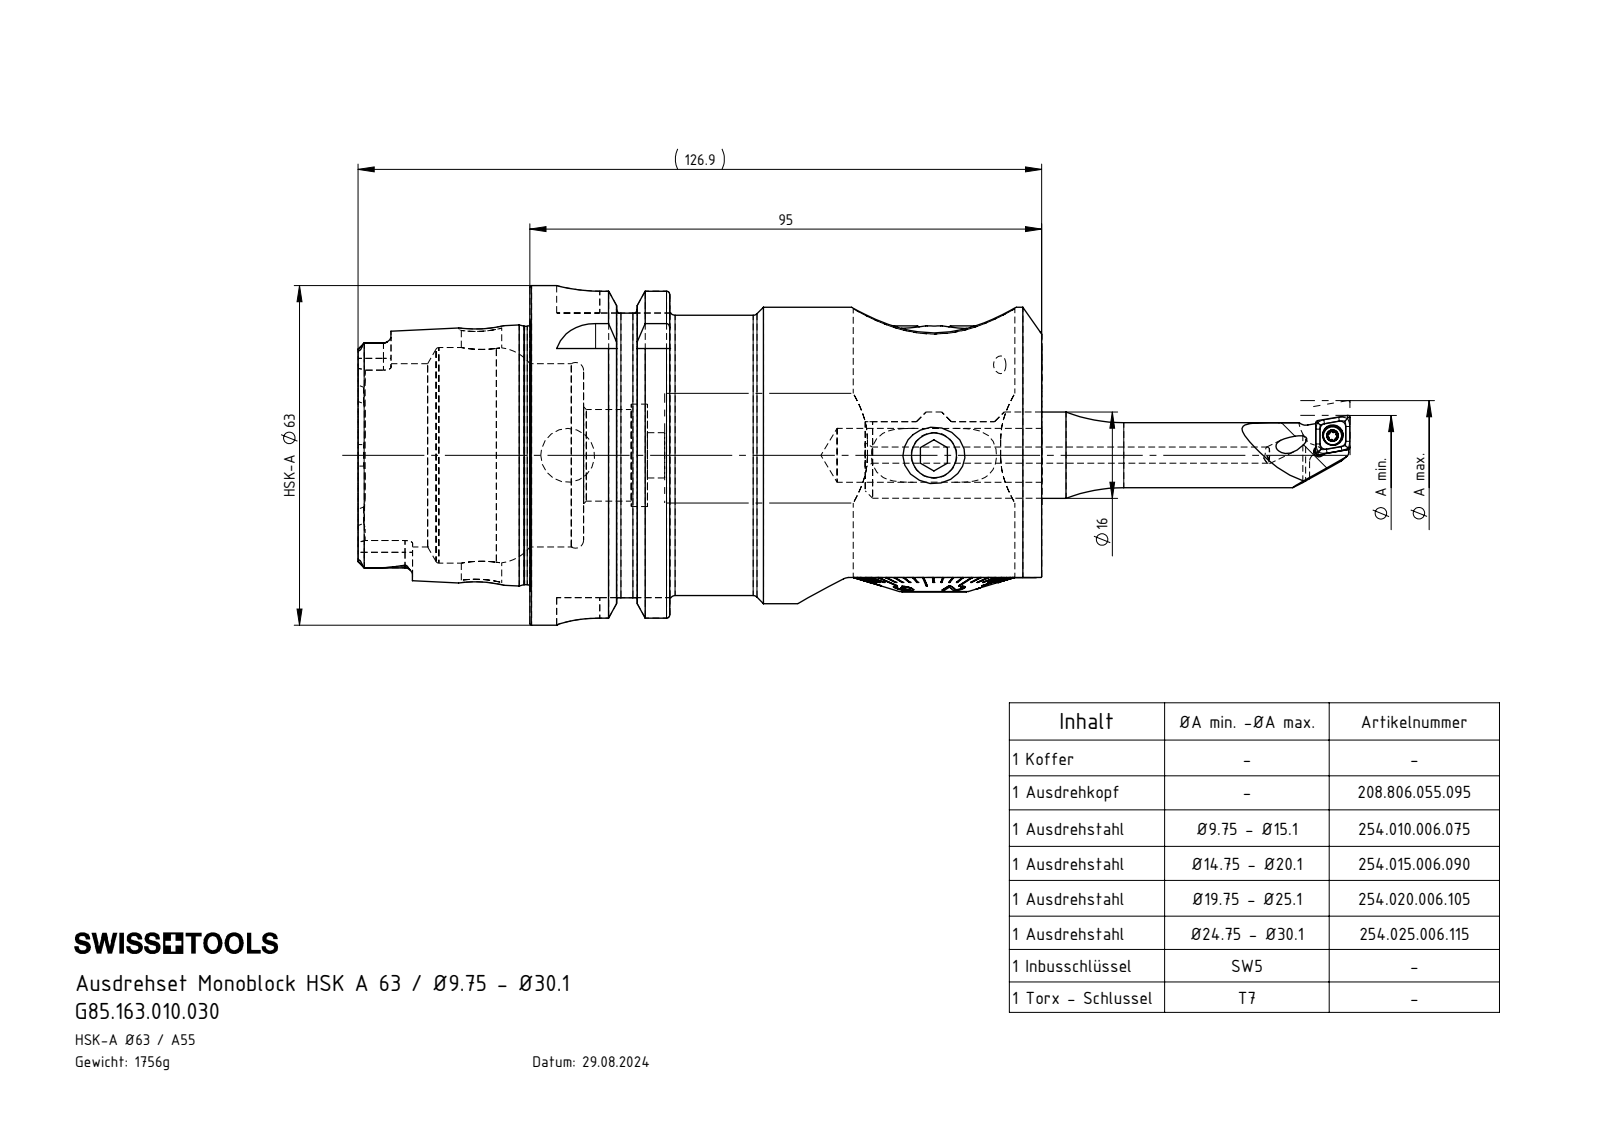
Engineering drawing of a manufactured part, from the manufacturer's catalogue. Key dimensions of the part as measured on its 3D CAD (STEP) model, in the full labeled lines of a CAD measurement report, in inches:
Part name (STEP PRODUCT): G85.163.010.030; B20-WCA.K11.105; A55-BG1.DA4.041; A55-BG2.012.006_B (+8 more)
STEP written by: SolidWorks 2022 (AUTOMOTIVE_DESIGN)
Units: inches
Bodies: 28 solids, 1422 faces (518 planar, 339 cylindrical, 565 other)
Overall size (bounding box): 9.386 × 4.996 × 2.48
Volume: 16.76 in³ · Surface area: 123.5 in²
Round holes (diameter × count): ⌀0.118 ×8, ⌀0.081 ×4, ⌀0.11 ×4, ⌀0.152 ×4, ⌀0.079 ×3, ⌀0.335 ×3, ⌀0.394 ×2, ⌀0.063 ×1, ⌀0.083 ×1, ⌀0.13 ×1, ⌀0.165 ×1, ⌀0.295 ×1
Round bosses / shafts (diameter × count): ⌀0.63 ×4, ⌀0.134 ×4, ⌀0.098 ×4, ⌀0.394 ×3, ⌀0.709 ×2, ⌀2.48 ×1, ⌀2.165 ×1, ⌀2.163 ×1
Partial cylindrical surfaces — rounded edges, fillets, slot ends (radius × count): R0.008 ×24, R0.014 ×17, R0.055 ×10, R0.014 ×7, R0.013 ×6, R0.023 ×6, R0.315 ×6, R0.02 ×4
Main face-to-face distances: 3.74, 1.256, 4.996, 0.63, 2.278, 1.022, 2.719, 1.648, 0.392, 3.348
Hole centre spacings: 0.571, 0.153, 0.157, 0.285, 1.683, 0.013, 0.153, 0.157
